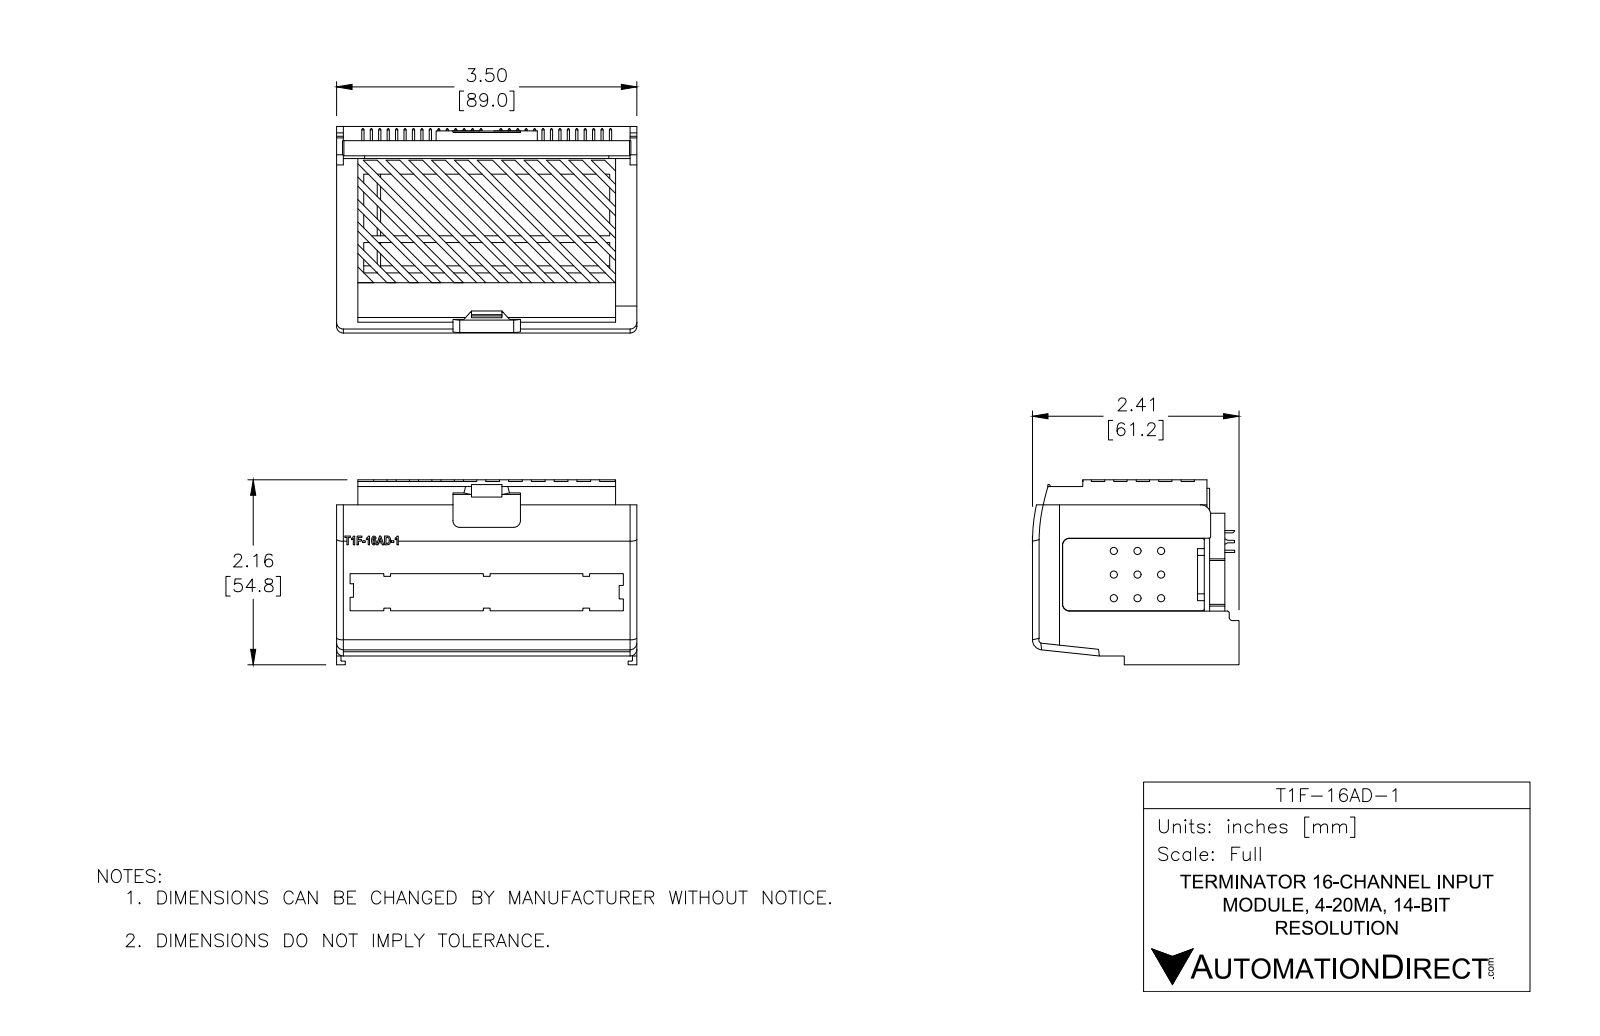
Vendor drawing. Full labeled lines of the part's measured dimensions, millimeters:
Part name (STEP PRODUCT): T1F-16AD-1
STEP written by: SolidWorks 2013 (AUTOMOTIVE_DESIGN)
Units: millimetres
Bodies: 1 solid, 646 faces (450 planar, 181 cylindrical, 15 other)
Overall size (bounding box): 88.7 × 65.1 × 61.36
Volume: 45 450 mm³ · Surface area: 54 522 mm²
Round holes (diameter × count): ⌀3 ×16
Round bosses / shafts (diameter × count): ⌀0.7 ×56
Partial cylindrical surfaces — rounded edges, fillets, slot ends (radius × count): R3.5 ×18, R1 ×5, R0.25 ×3, R0.55 ×3, R1.5 ×2, R8 ×1, R10 ×1, R18 ×1
Main face-to-face distances: 2, 86.7, 55.35, 0.5, 59.8, 88.7, 1.5, 55.26, 53.35, 84.7
Hole centre spacings: 5.15, 10.3, 15.45, 20.6, 25.75, 30.9, 36.05, 41.2
